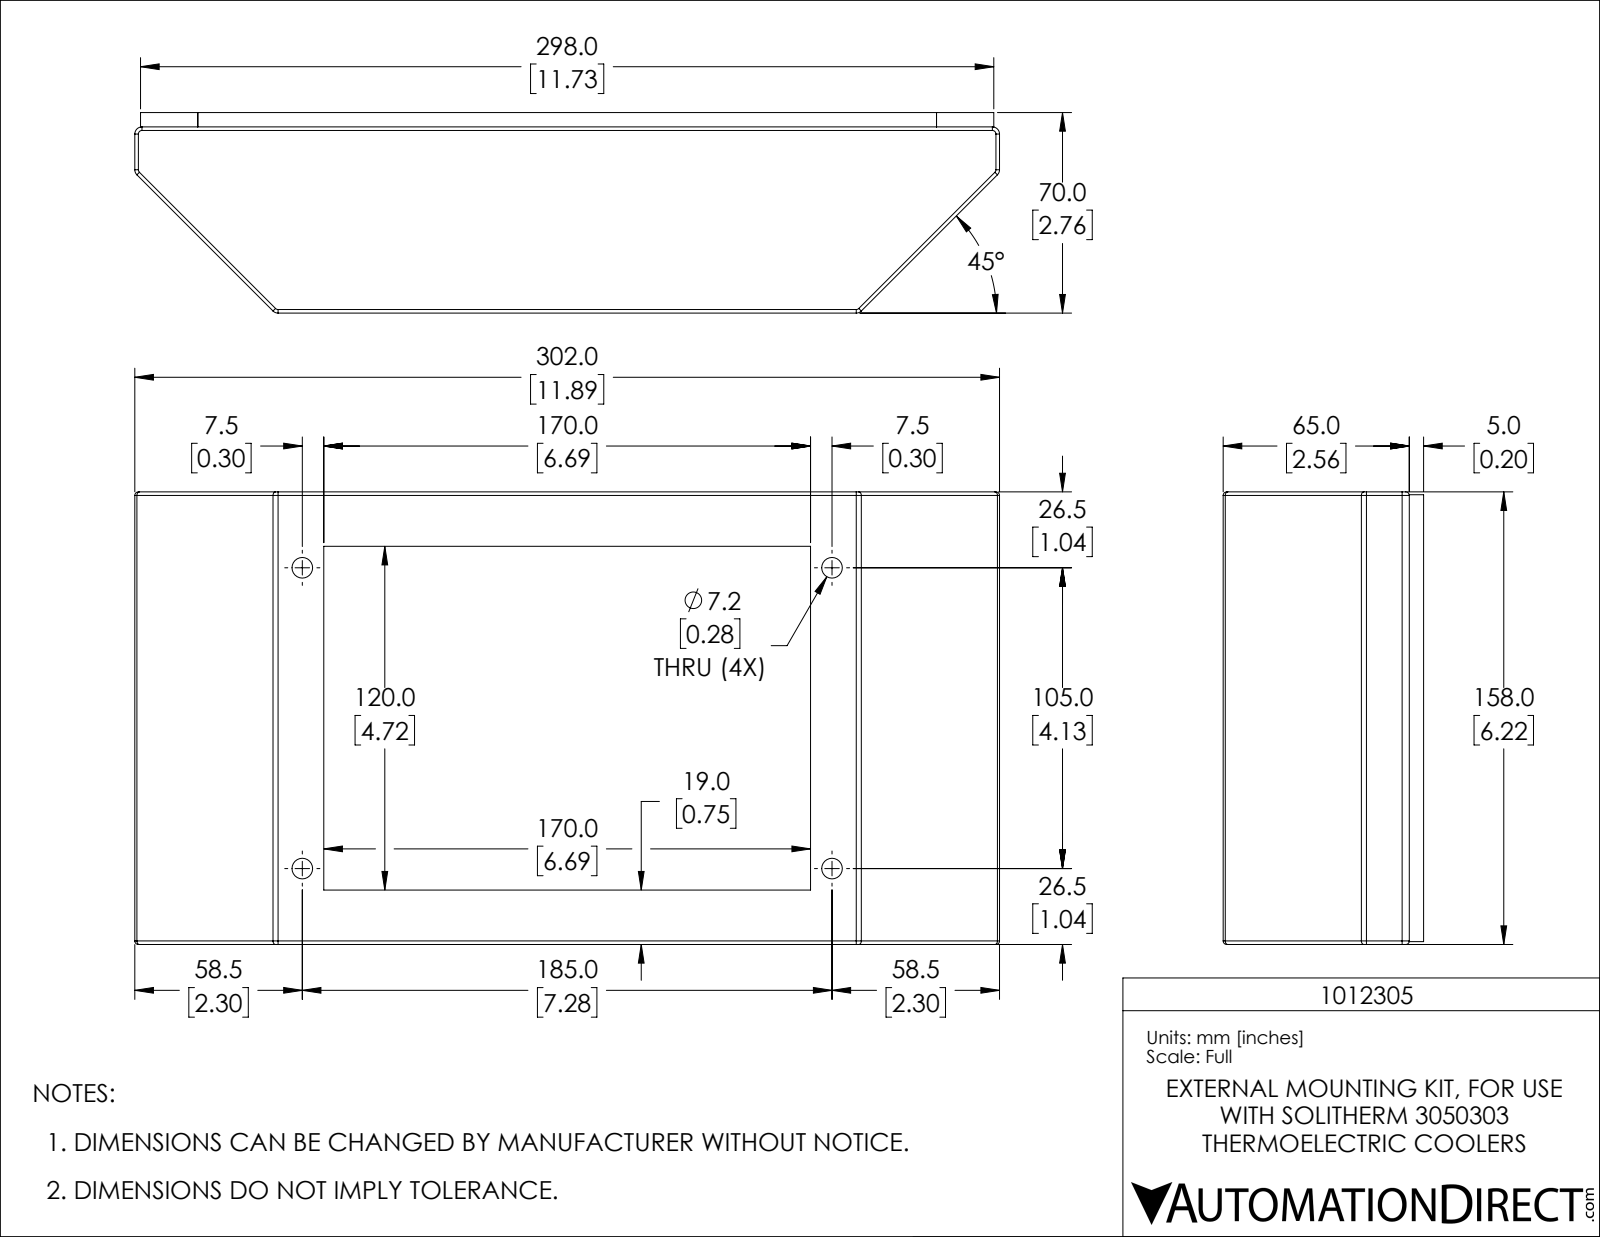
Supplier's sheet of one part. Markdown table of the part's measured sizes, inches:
| quantity | value |
| --- | --- |
| part name | 1012305 |
| STEP written by | SolidWorks 2019 (AUTOMOTIVE_DESIGN) |
| units | inches |
| bodies | 17 solids, 328 faces (264 planar, 44 cylindrical, 20 other) |
| overall size | 11.89 × 6.22 × 2.756 |
| volume | 43.66 in³ |
| surface area | 533 in² |
| round holes (diameter × count) | 0.197 × 4, 0.256 × 4, 0.283 × 4 |
| round bosses / shafts (diameter × count) | 0.402 × 4, 0.35 × 4 |
| partial cylindrical surfaces (radius × count) | 0.049 × 12, 0.039 × 6, 0.098 × 6 |
| main face-to-face distances | 0.059, 0.453, 0.394, 6.161, 2.5, 6.102, 5.768, 5.709, 5.315, 0.393 |
| hole center spacings | 1.969, 4.134, 4.579, 9.252, 10.133, 7.283, 8.375, 11.22 |
